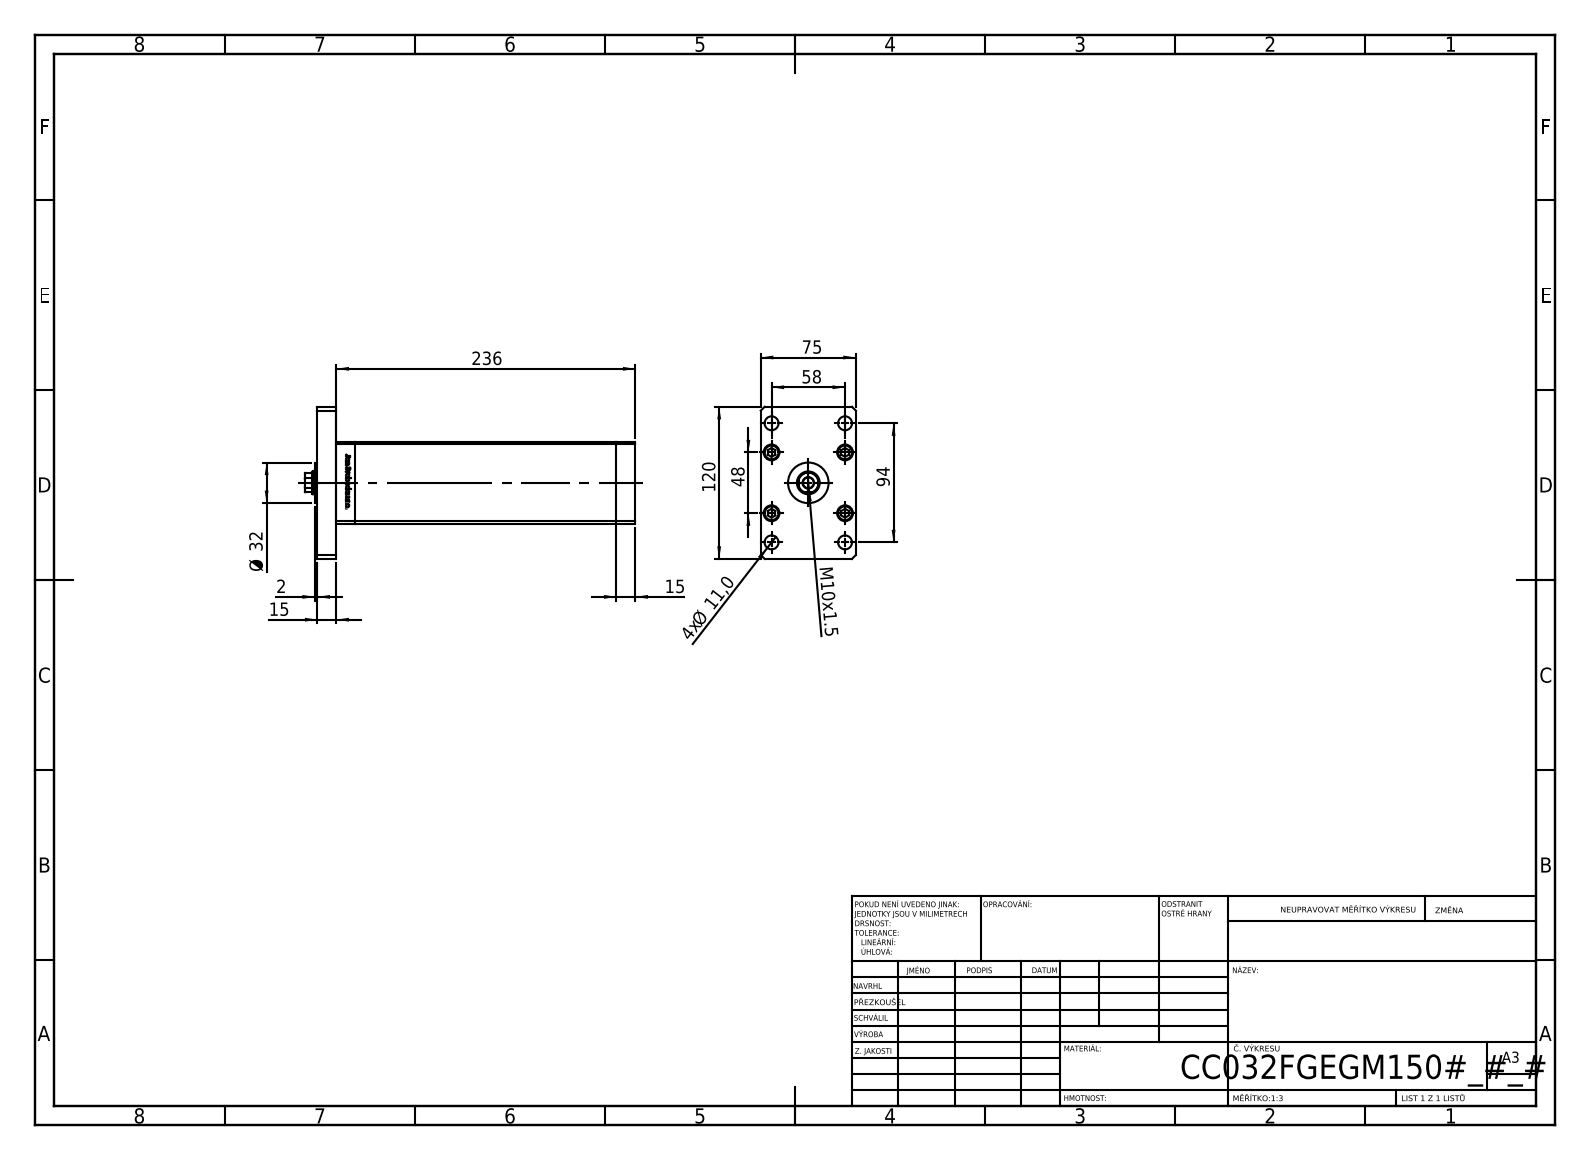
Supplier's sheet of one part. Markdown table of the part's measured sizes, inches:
| quantity | value |
| --- | --- |
| part name | ALLEN BOLT; V220C_F_MIDDLE; V220C_FRONT_F; V220C BACK_F (+2 more) |
| STEP written by | SolidWorks 2019 (CONFIG_CONTROL_DESIGN) |
| units | inches |
| bodies | 19 solids, 1308 faces (515 planar, 187 cylindrical, 606 other) |
| overall size | 10.276 × 4.724 × 2.953 |
| volume | 69.38 in³ |
| surface area | 297.5 in² |
| round holes (diameter × count) | 0.354 × 5, 0.531 × 5, 0.315 × 4, 0.433 × 4, 0.492 × 4, 0.079 × 2, 0.518 × 2, 0.335 × 1, 0.709 × 1, 0.768 × 1 |
| round bosses / shafts (diameter × count) | 0.492 × 5, 0.315 × 5, 1.26 × 1 |
| partial cylindrical surfaces (radius × count) | 0.037 × 2, 0.335 × 1 |
| main face-to-face distances | 0.591, 2.953, 2.559, 8.701, 9.291, 1.181, 8.11, 9.882, 0.512, 2.146 |
| hole center spacings | 0.945, 0.906, 1.482, 2.174, 2.283, 2.456, 2.795, 3.609 |
